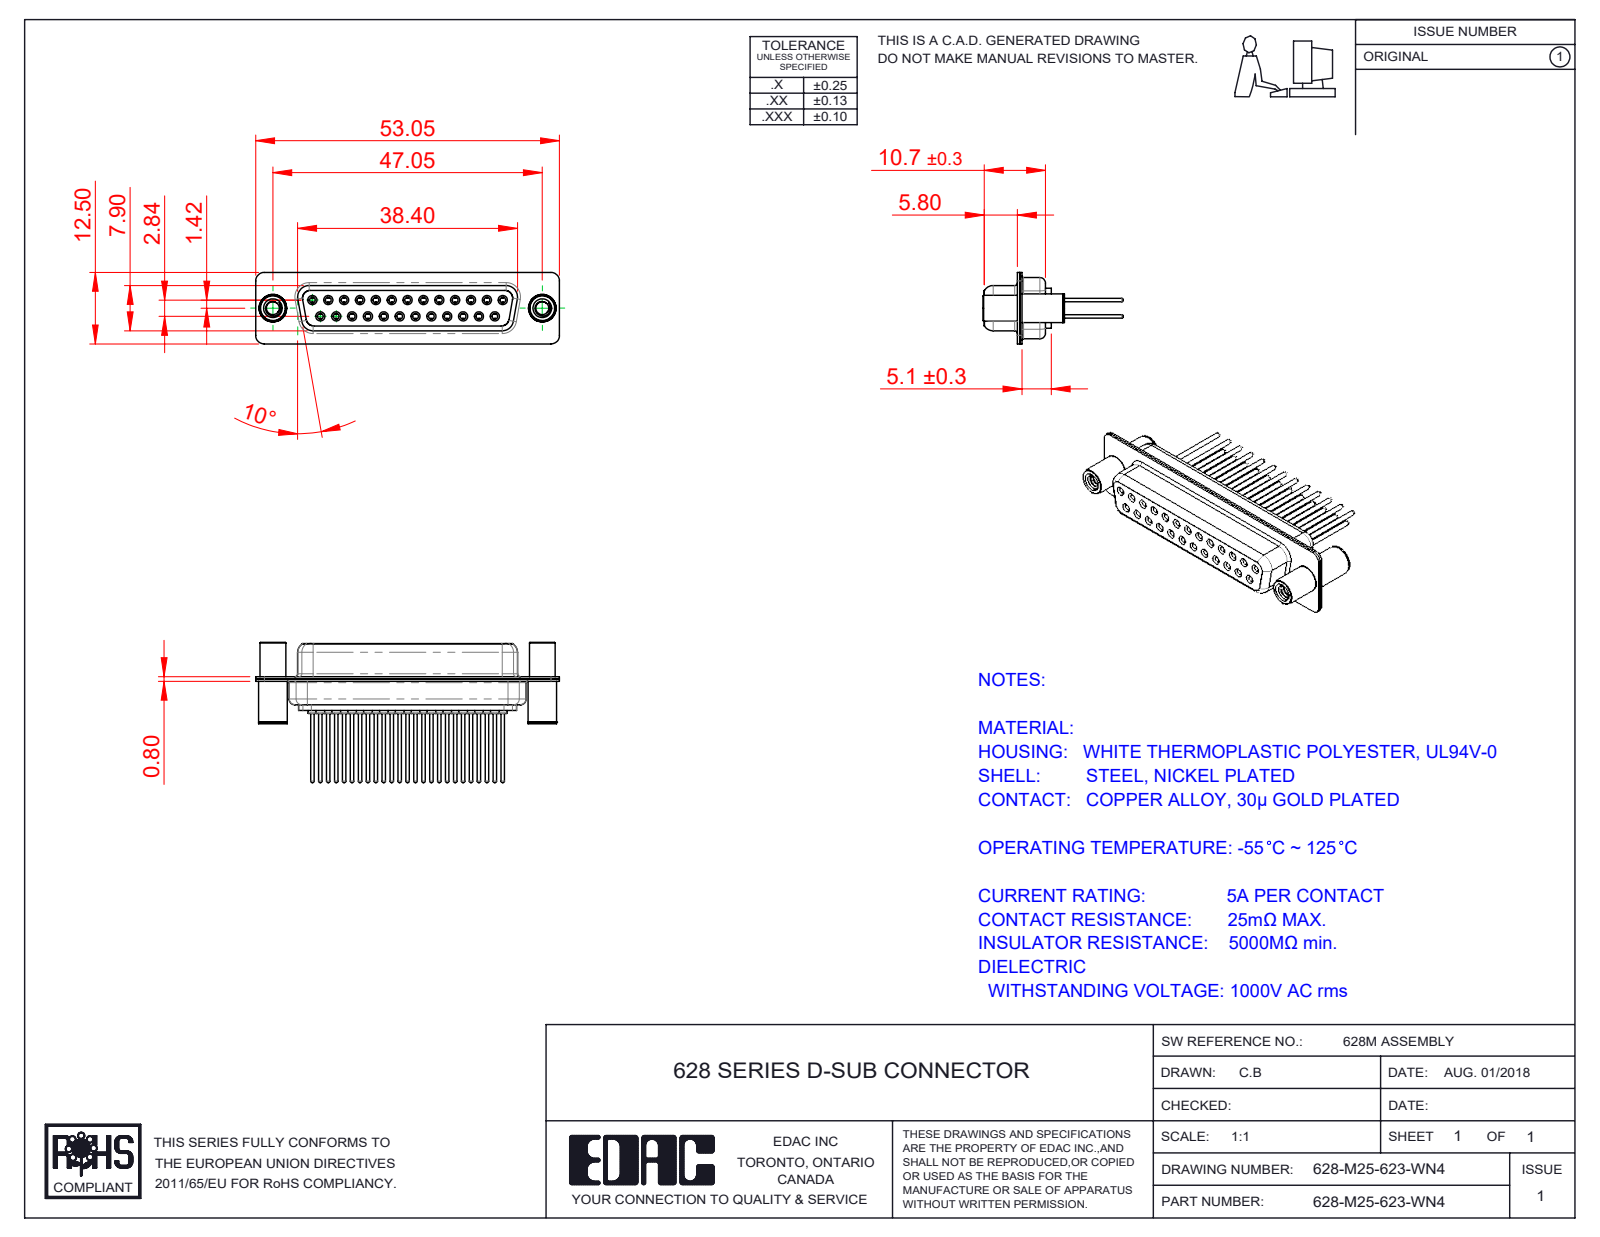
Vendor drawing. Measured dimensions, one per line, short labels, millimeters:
name: 628M Shell Front_25 Contacts; 628M Shell Rear_25 Contacts; 628M Contact Row 1_23; 628M Contact Row 2_23 (+3 more)
written by: SolidWorks 2020 (CONFIG_CONTROL_DESIGN)
unit: mm
bodies: 30 solids, 1740 faces (448 planar, 664 cylindrical, 628 other)
size: 53.05 × 24.47 × 12.5
volume: 4 074 mm³; area: 9 990 mm²
holes: 25× ⌀1, 25× ⌀1.1, 25× ⌀1.7, 25× ⌀1.8, 25× ⌀2, 2× ⌀2.26, 2× ⌀3.26, 2× ⌀4, 2× ⌀4.8
bosses: 25× ⌀2.2, 25× ⌀1.6, 25× ⌀1.5, 25× ⌀0.6, 2× ⌀5, 2× ⌀4.9, 2× ⌀4.5
rounds: 16× R1.5, 12× R2, 8× R1.35, 8× R1.6, 4× R0.25, 4× R0.5, 4× R0.6, 4× R0.65
face distances: 0.4, 1.4, 0.45, 8.45, 8.9, 1.8, 6.2, 7.05, 1, 1.85
hole spacings: 3.16, 2.77, 5.54, 8.31, 11.08, 13.85, 5.04, 7.49
